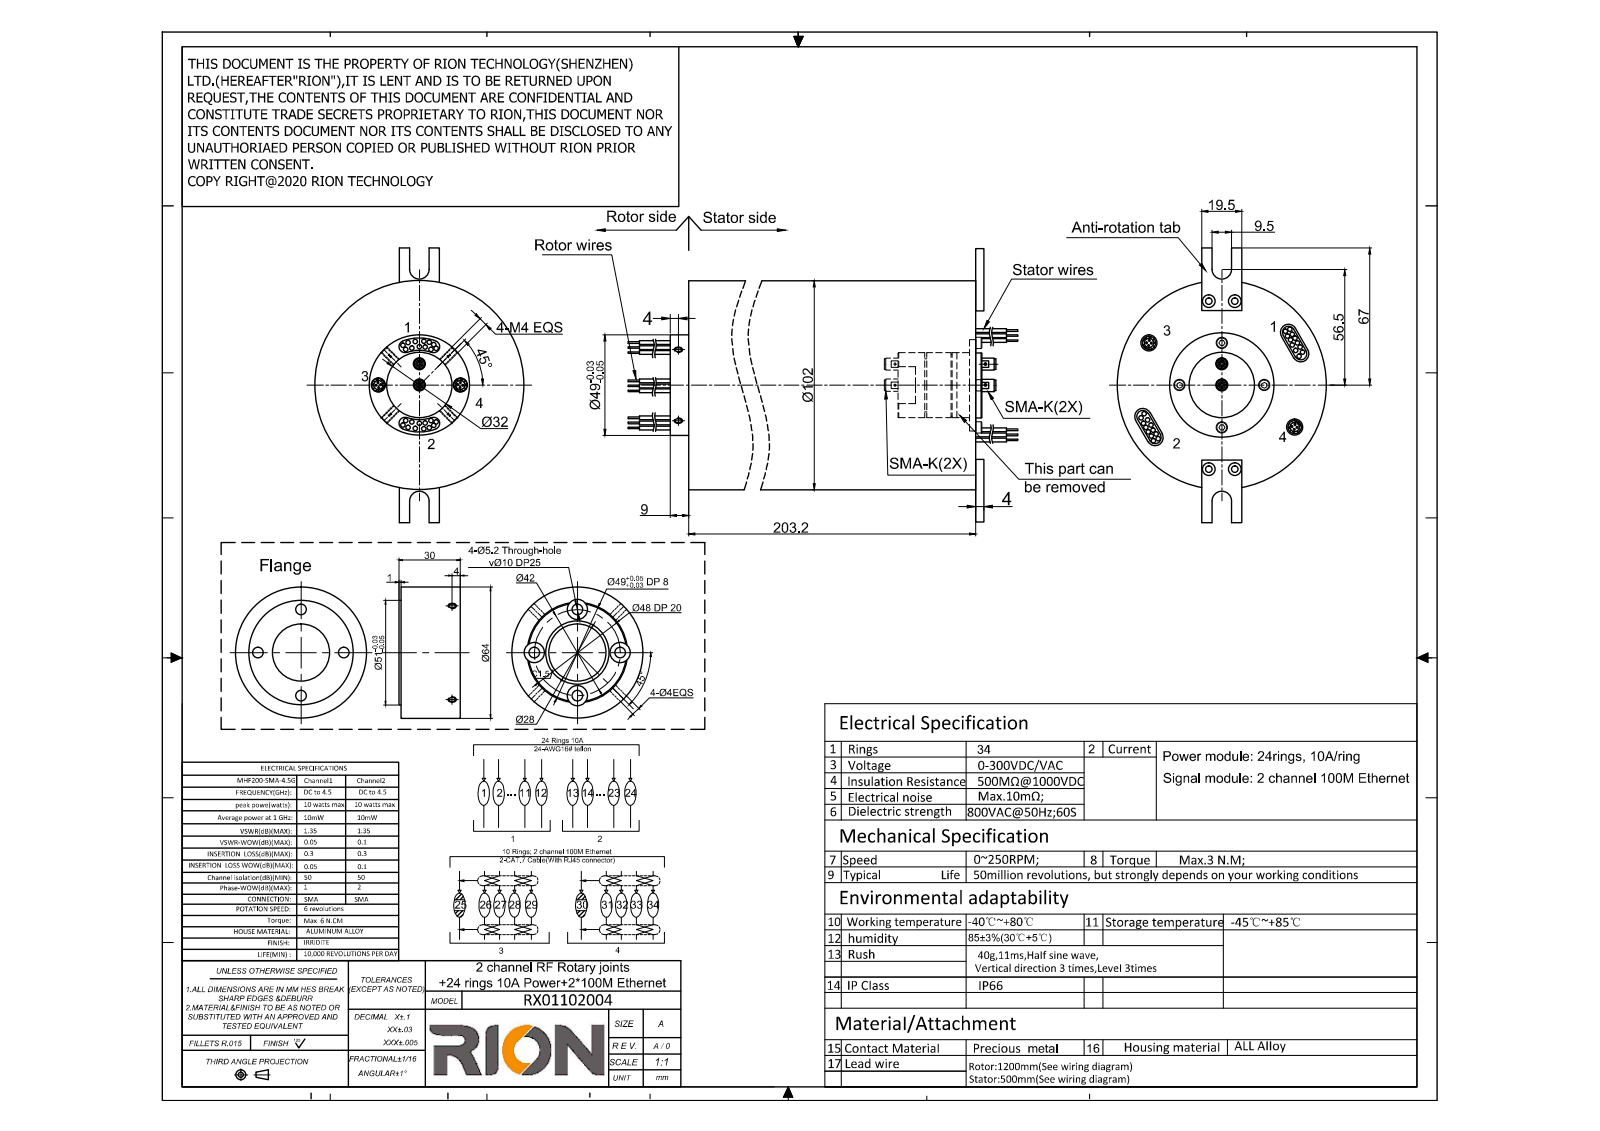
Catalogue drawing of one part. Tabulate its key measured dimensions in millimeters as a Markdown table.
| quantity | value |
| --- | --- |
| part name | RX01102004(1) |
| STEP written by | SolidWorks 2014 (AUTOMOTIVE_DESIGN) |
| units | millimeters |
| bodies | 2 solids, 317 faces (129 planar, 172 cylindrical, 16 other) |
| overall size | 272.2 × 134 × 102 |
| volume | 1 691 000 mm³ |
| surface area | 99 735 mm² |
| round holes (diameter × count) | 3.2 × 4, 3.3 × 4, 7 × 2, 8 × 2, 32 × 1 |
| round bosses / shafts (diameter × count) | 2.1 × 48, 6.5 × 4, 6 × 4, 5.5 × 4, 102 × 1, 49 × 1, 31.8 × 1, 5.2 × 1 |
| partial cylindrical surfaces (radius × count) | 3 × 8, 4.75 × 2, 17 × 1, 23 × 1 |
| main face-to-face distances | 203.2, 1, 215.2, 214.2, 9, 4, 206.2, 3, 8, 207.2 |
| hole center spacings | 12.7, 20, 25.71, 41, 41.45, 41.53, 43.14, 43.29 |
